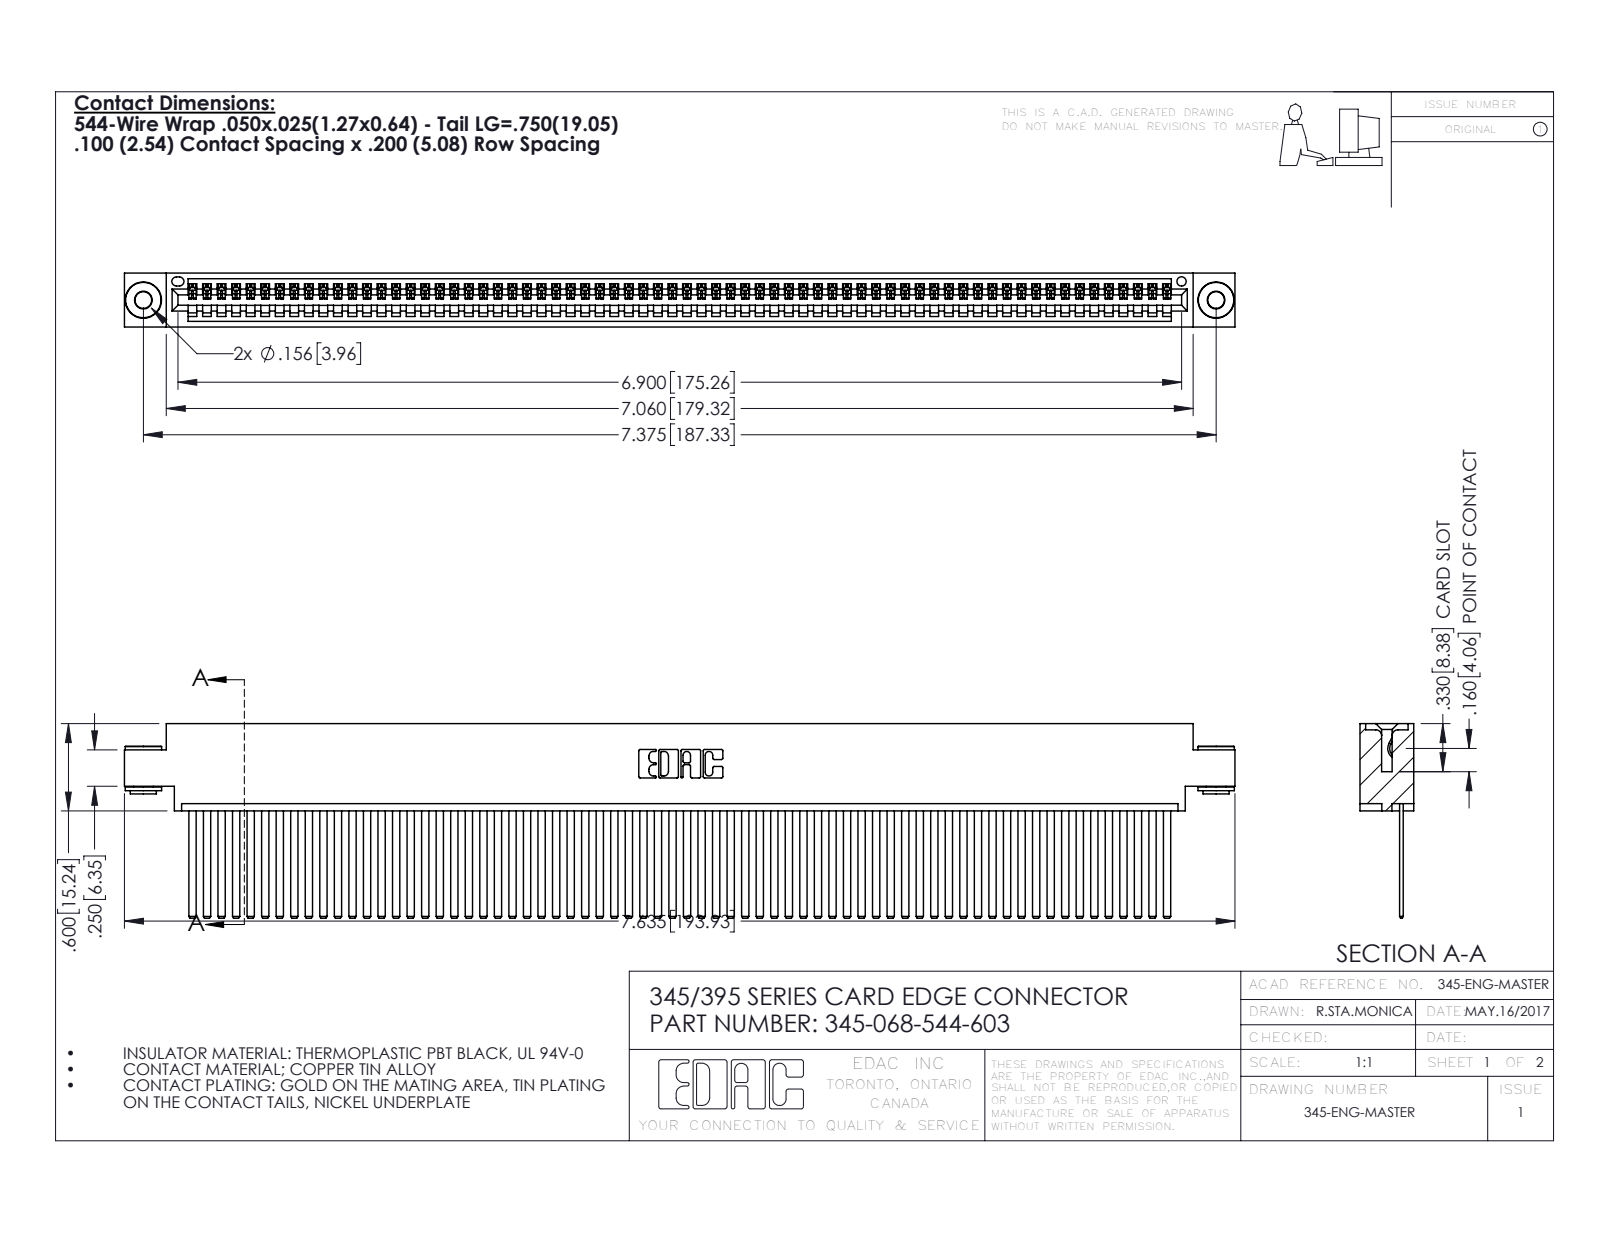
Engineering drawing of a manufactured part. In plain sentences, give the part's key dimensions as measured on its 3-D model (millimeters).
The part is named "345-250-002_345-250-002-102; 345-292-001_345-293-144; 345 Part_0.170 Offset - 0.156 Dia-TH; 345-068-544-603". Its 3-D file was written by "SolidWorks 2016 (CONFIG_CONTROL_DESIGN)". It is 71 solids with 3704 faces: 2542 planar, 1154 cylindrical and 8 other. Overall it measures 193.9 by 34 by 9.4 millimeters. Its volume is 19 320 cubic millimeters and its surface area 28 740 square millimeters. Round holes: 2 of diameter 2.9, 2 of diameter 4, 1 of diameter 1.6. Round bosses or shafts: 2 of diameter 6.4, 2 of diameter 4.6, 2 of diameter 3.5. Partial cylindrical surfaces (rounded edges, fillets, slot ends): 136 of radius 0.2, 22 of radius 0.3, 6 of radius 0.2, 6 of radius 0.8, 3 of radius 0.7, 2 of radius 0.8, 2 of radius 1, 1 of radius 0.4. The main face-to-face distances are 1.8, 7.6, 0.6, 2.5, 6.9, 9.4, 5.1, 5.7, 4.4, 3.8. The hole center spacings are 6.9, 181.3, 187.3.
